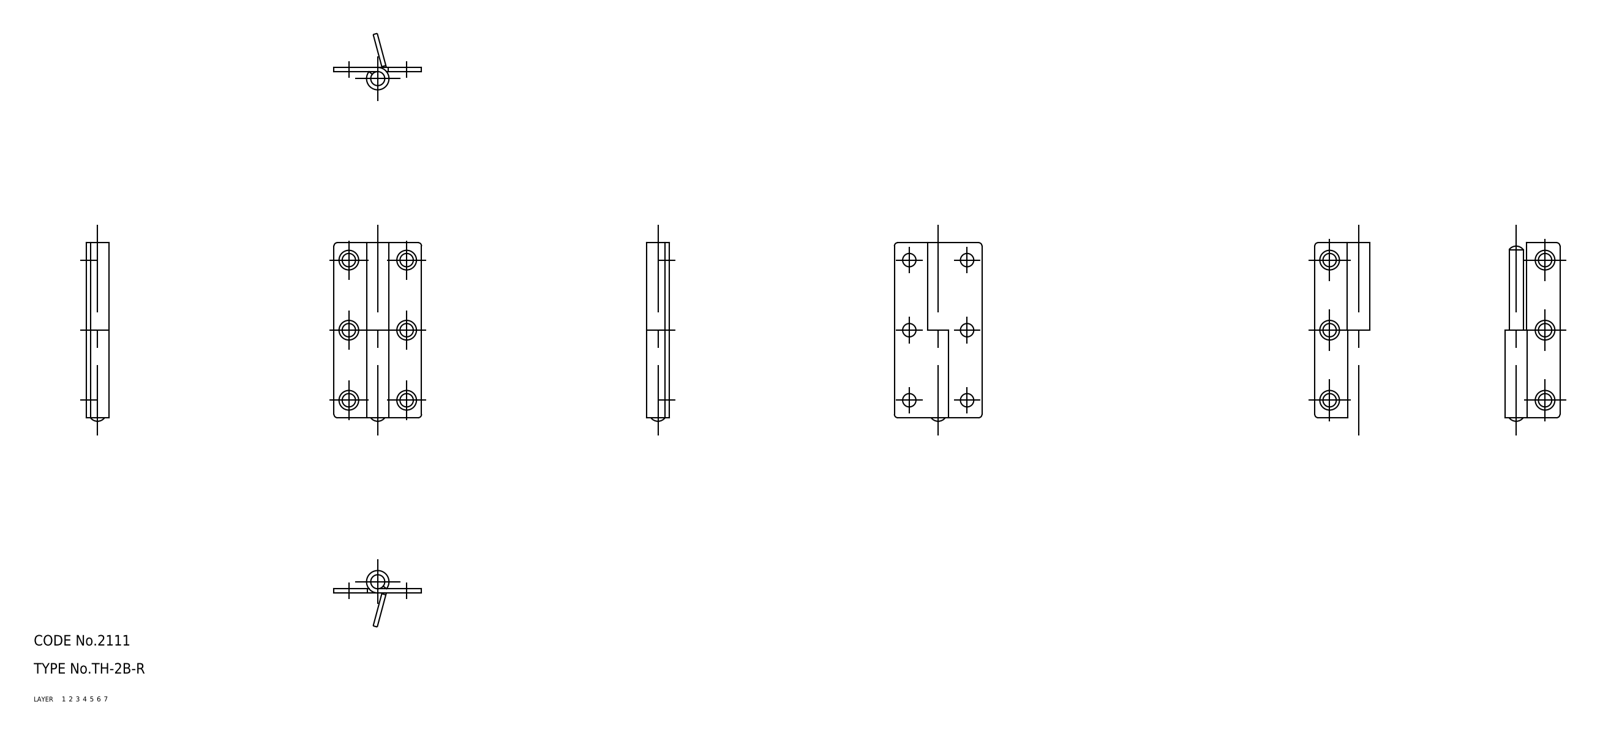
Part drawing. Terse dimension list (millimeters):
name: shaft; hinge piece_B; hinge piece_A; TH_2B_R_7308_36
written by: CADfix (AUTOMOTIVE_DESIGN)
unit: mm
bodies: 3 solids, 52 faces (0 planar, 0 cylindrical, 52 other)
size: 51 × 25 × 6.4
volume: 2 659 mm³; area: 4 513 mm²
